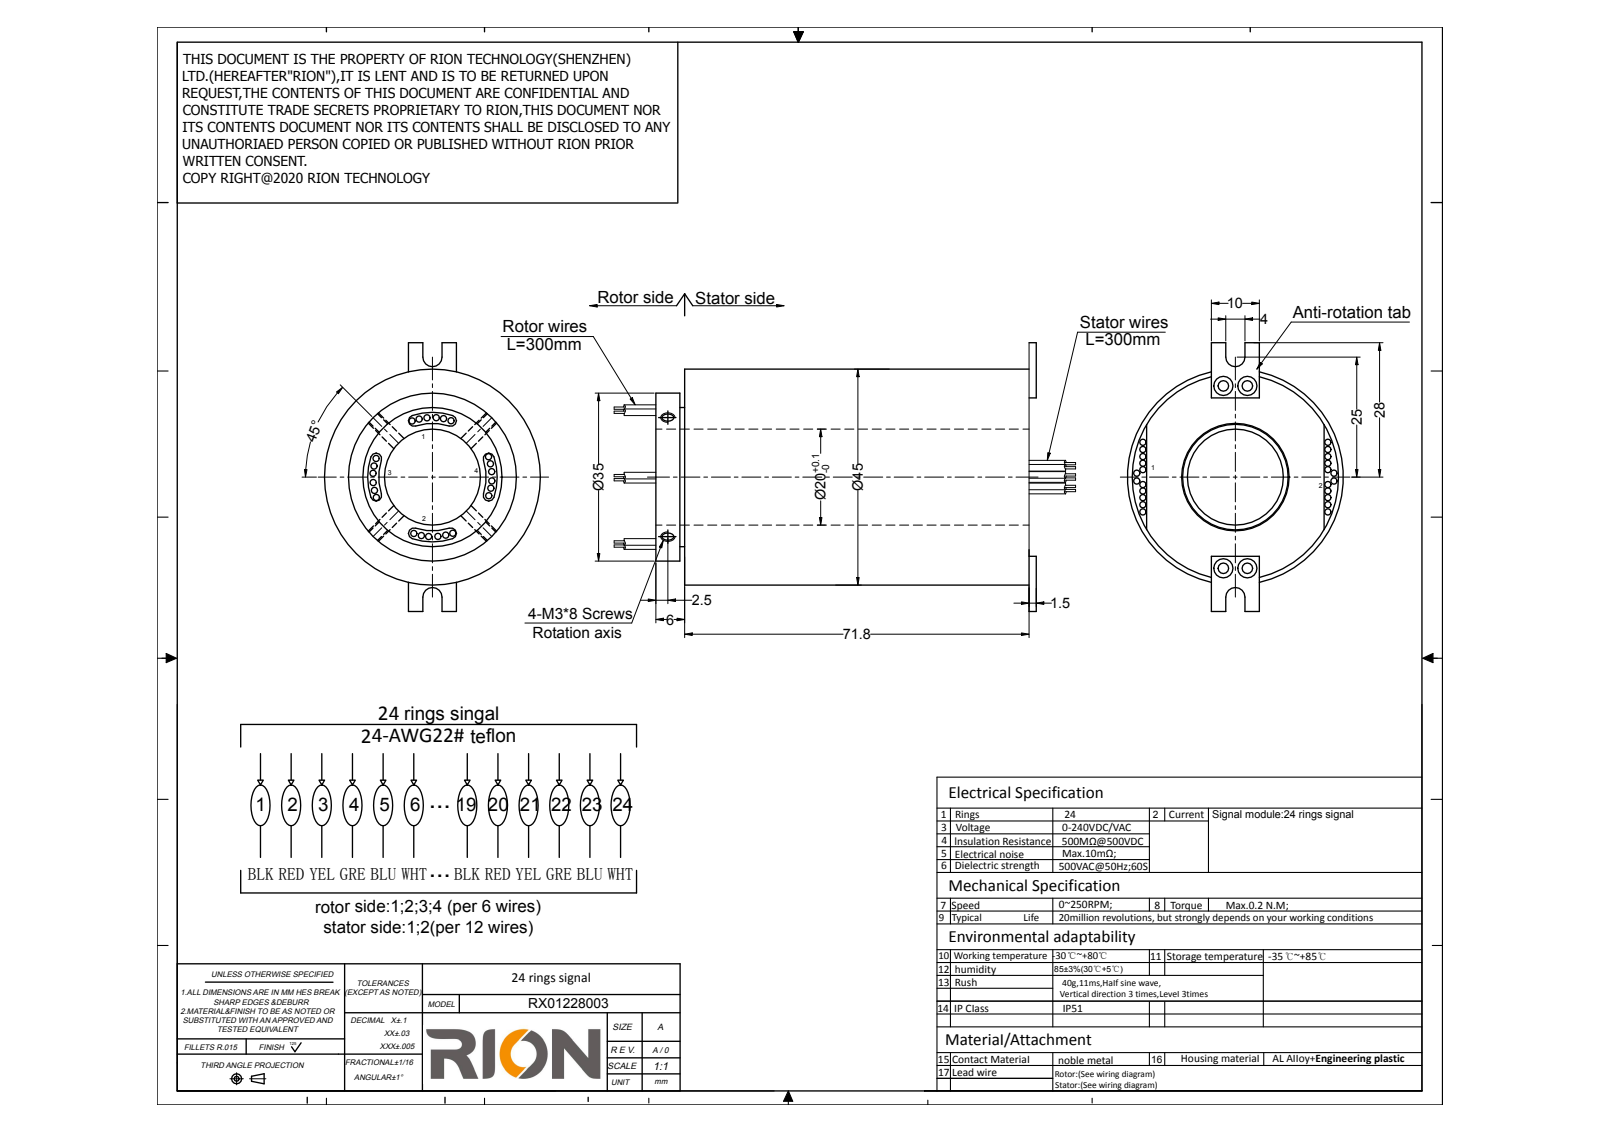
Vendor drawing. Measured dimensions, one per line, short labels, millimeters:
written by: SolidWorks 2014 (CONFIG_CONTROL_DESIGN)
unit: mm
bodies: 1 solid, 271 faces (103 planar, 152 cylindrical, 16 other)
size: 95.8 × 56 × 45
volume: 95 679 mm³; area: 23 400 mm²
holes: 4× ⌀1.6, 4× ⌀2.2, 4× ⌀2.5, 1× ⌀20, 1× ⌀22.2, 1× ⌀43
bosses: 24× ⌀1.3, 24× ⌀1.25, 1× ⌀45, 1× ⌀42.9, 1× ⌀35, 1× ⌀29, 1× ⌀22
rounds: 8× R1, 2× R2
face distances: 71.8, 6, 77.8, 1, 5, 72.8, 79.3, 74.3, 73.3, 1.5
hole spacings: 19.16, 5, 38, 38.33
